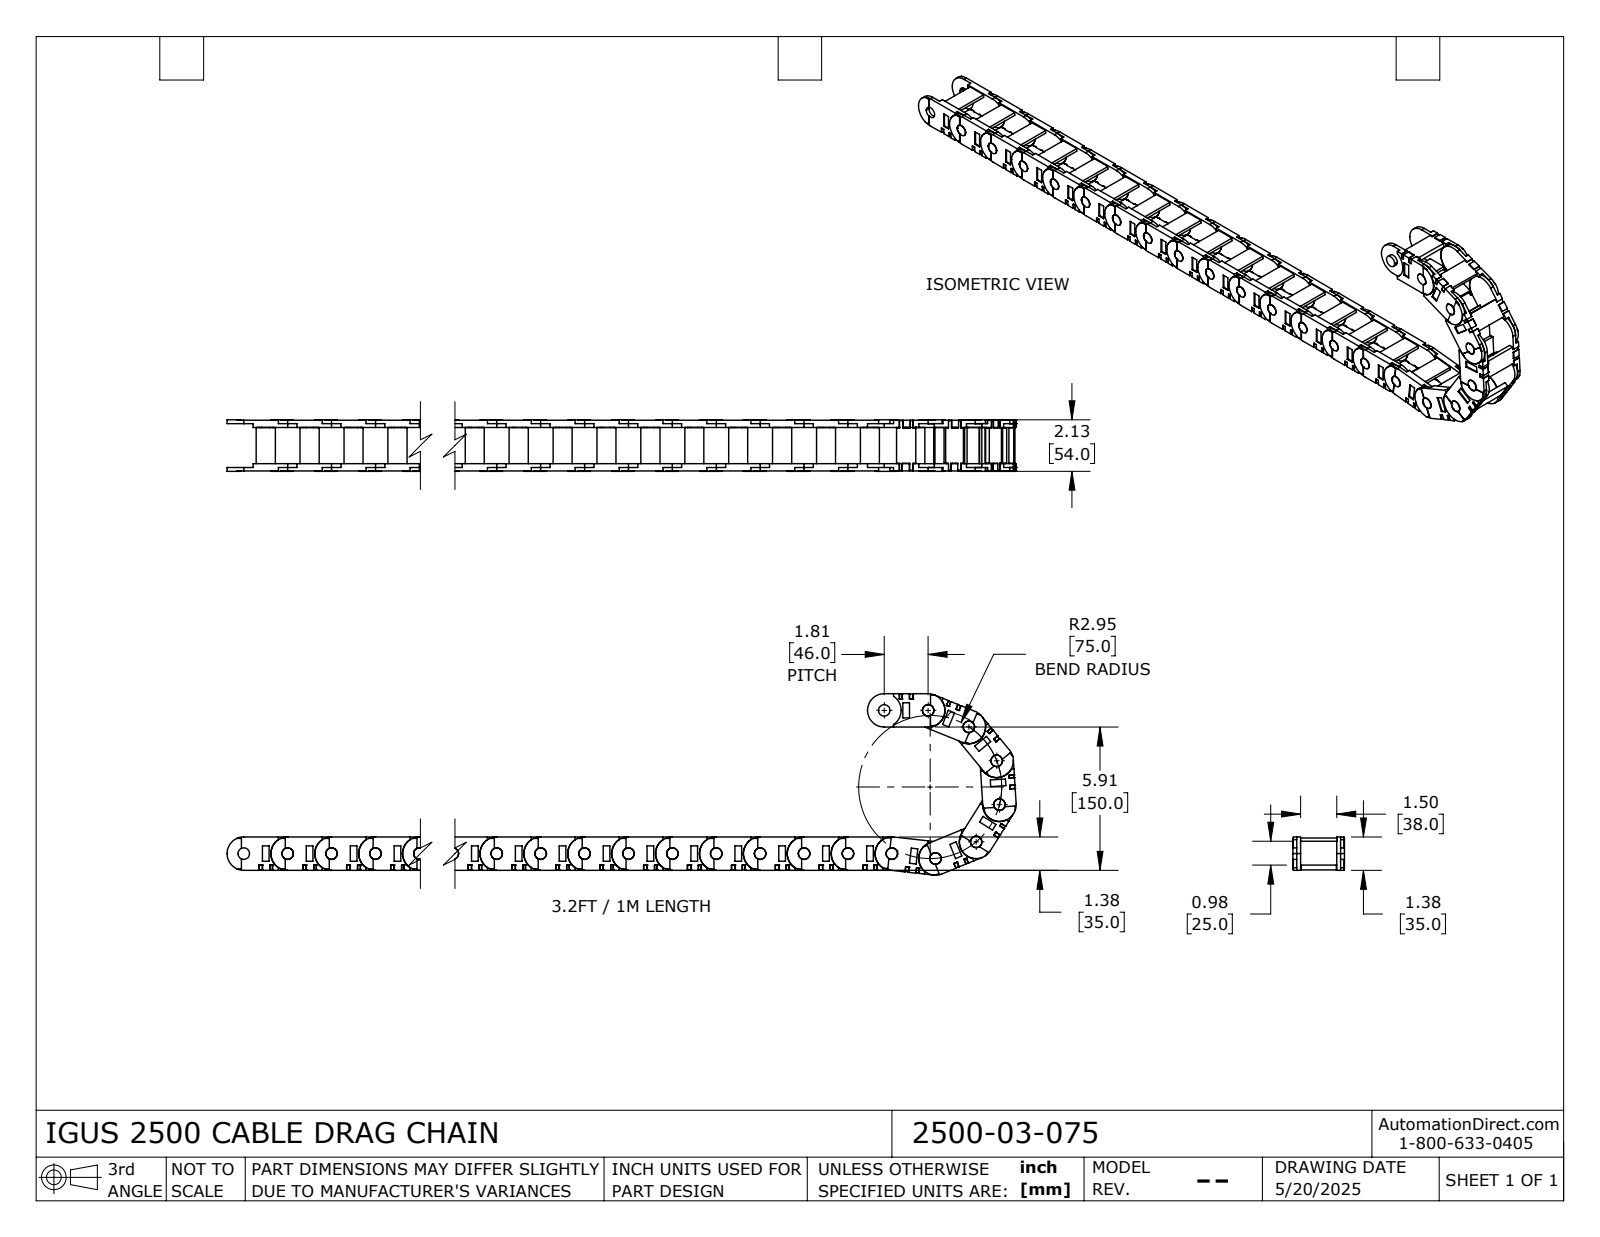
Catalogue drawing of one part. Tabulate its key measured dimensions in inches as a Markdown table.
| quantity | value |
| --- | --- |
| part name | 2500_03_075 |
| STEP written by | SolidWorks 2024 (AUTOMOTIVE_DESIGN) |
| units | inches |
| bodies | 66 solids, 2398 faces (1870 planar, 528 cylindrical, 0 other) |
| overall size | 32.981 × 7.485 × 2.126 |
| volume | 40.89 in³ |
| surface area | 601.2 in² |
| round holes (diameter × count) | 0.473 × 22 |
| round bosses / shafts (diameter × count) | 0.472 × 22, 1.378 × 21 |
| partial cylindrical surfaces (radius × count) | 0.697 × 23, 0.689 × 2 |
| main face-to-face distances | 0.157, 1.654, 1.811, 0.142, 0.299, 1.795, 1.953, 1.496, 0.016, 2.094 |
| hole center spacings | 1.811, 3.622, 5.433, 7.244, 9.055, 10.866, 12.677, 14.488 |
